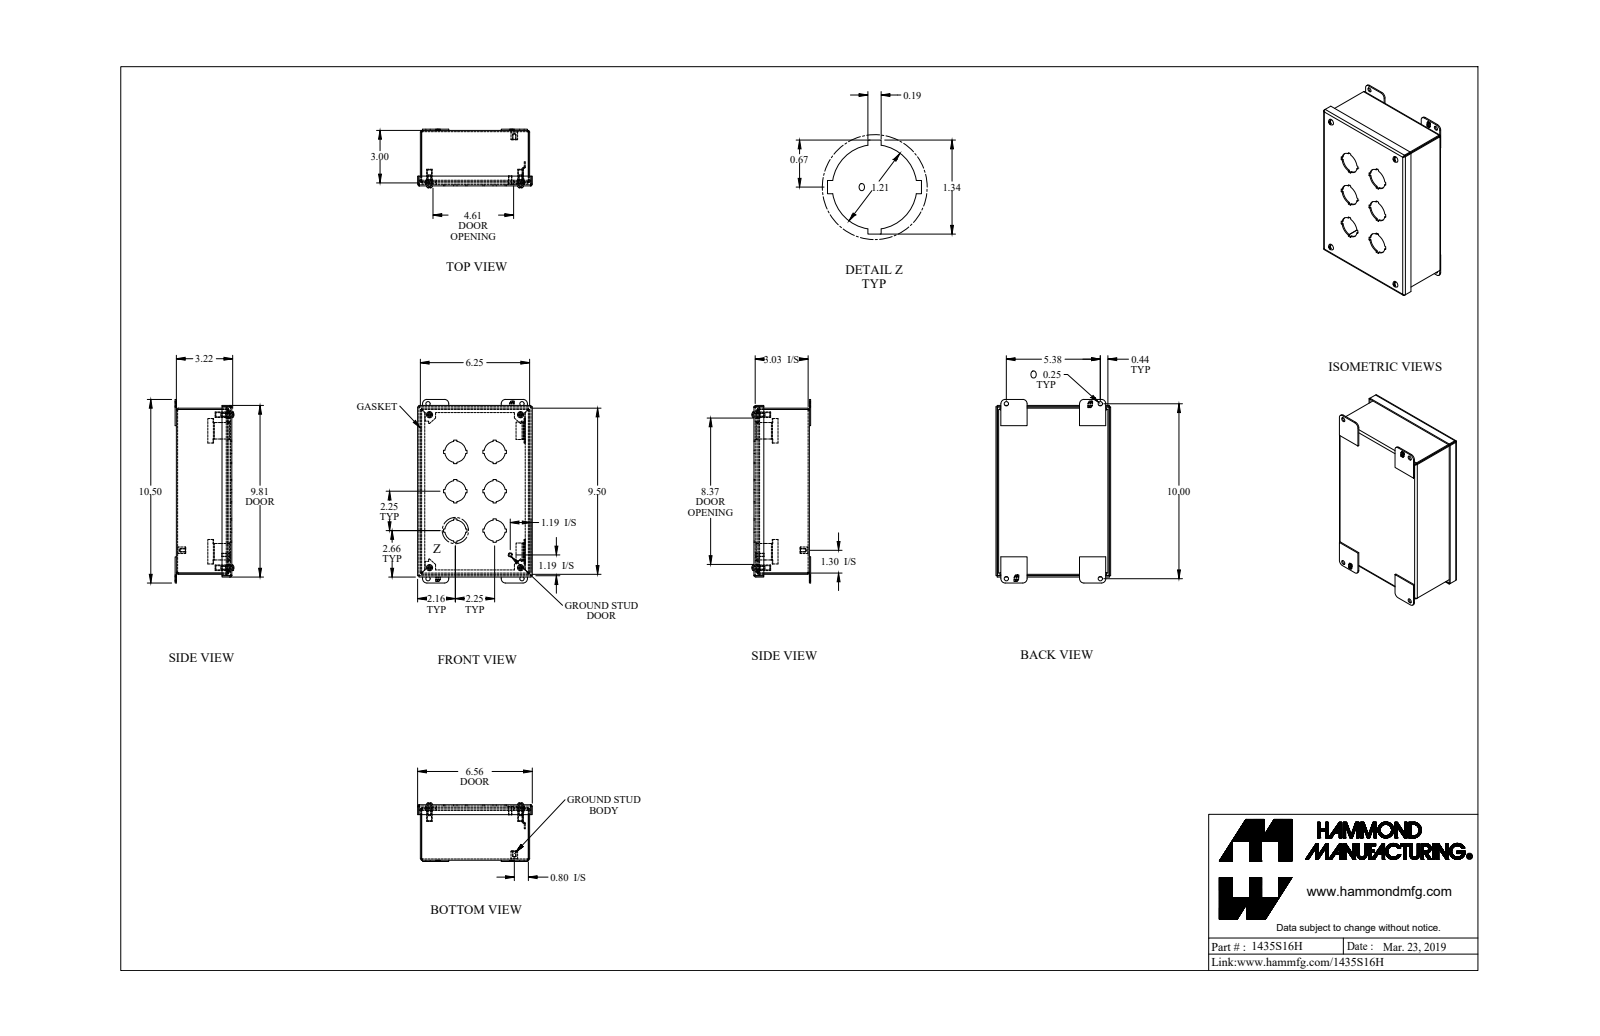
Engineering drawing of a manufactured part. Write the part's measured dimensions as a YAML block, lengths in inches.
part_name: "1435S16H_Default"
step_written_by: "SolidWorks 2019 (CONFIG_CONTROL_DESIGN)"
units: inches
bodies: {solids: 23, faces: 701, planar: 495, cylindrical: 176, other: 30}
overall_size: [10.5, 6.562, 3.354]
volume: 20.39
surface_area: 540.4
round_holes:
  - {diameter: 0.25, count: 8}
  - {diameter: 1.21, count: 6}
  - {diameter: 0.065, count: 4}
  - {diameter: 0.239, count: 4}
  - {diameter: 0.253, count: 4}
  - {diameter: 0.406, count: 4}
  - {diameter: 0.156, count: 1}
round_bosses_or_shafts:
  - {diameter: 0.19, count: 5}
  - {diameter: 0.406, count: 4}
  - {diameter: 0.315, count: 4}
  - {diameter: 0.148, count: 4}
  - {diameter: 0.375, count: 1}
  - {diameter: 0.25, count: 1}
partial_cylinders:
  - {radius: 0.036, count: 12}
  - {radius: 0.108, count: 12}
  - {radius: 0.25, count: 8}
  - {radius: 0.029, count: 4}
  - {radius: 0.086, count: 4}
  - {radius: 0.171, count: 4}
face_to_face_distances: [0.072, 3.1, 3.172, 3.028, 6.178, 9.428, 6.25, 6.106, 0.156, 6.334]
hole_center_spacings: [5.211, 5.212, 8.749, 8.75, 9.375, 2.25, 10.183, 10.183]
